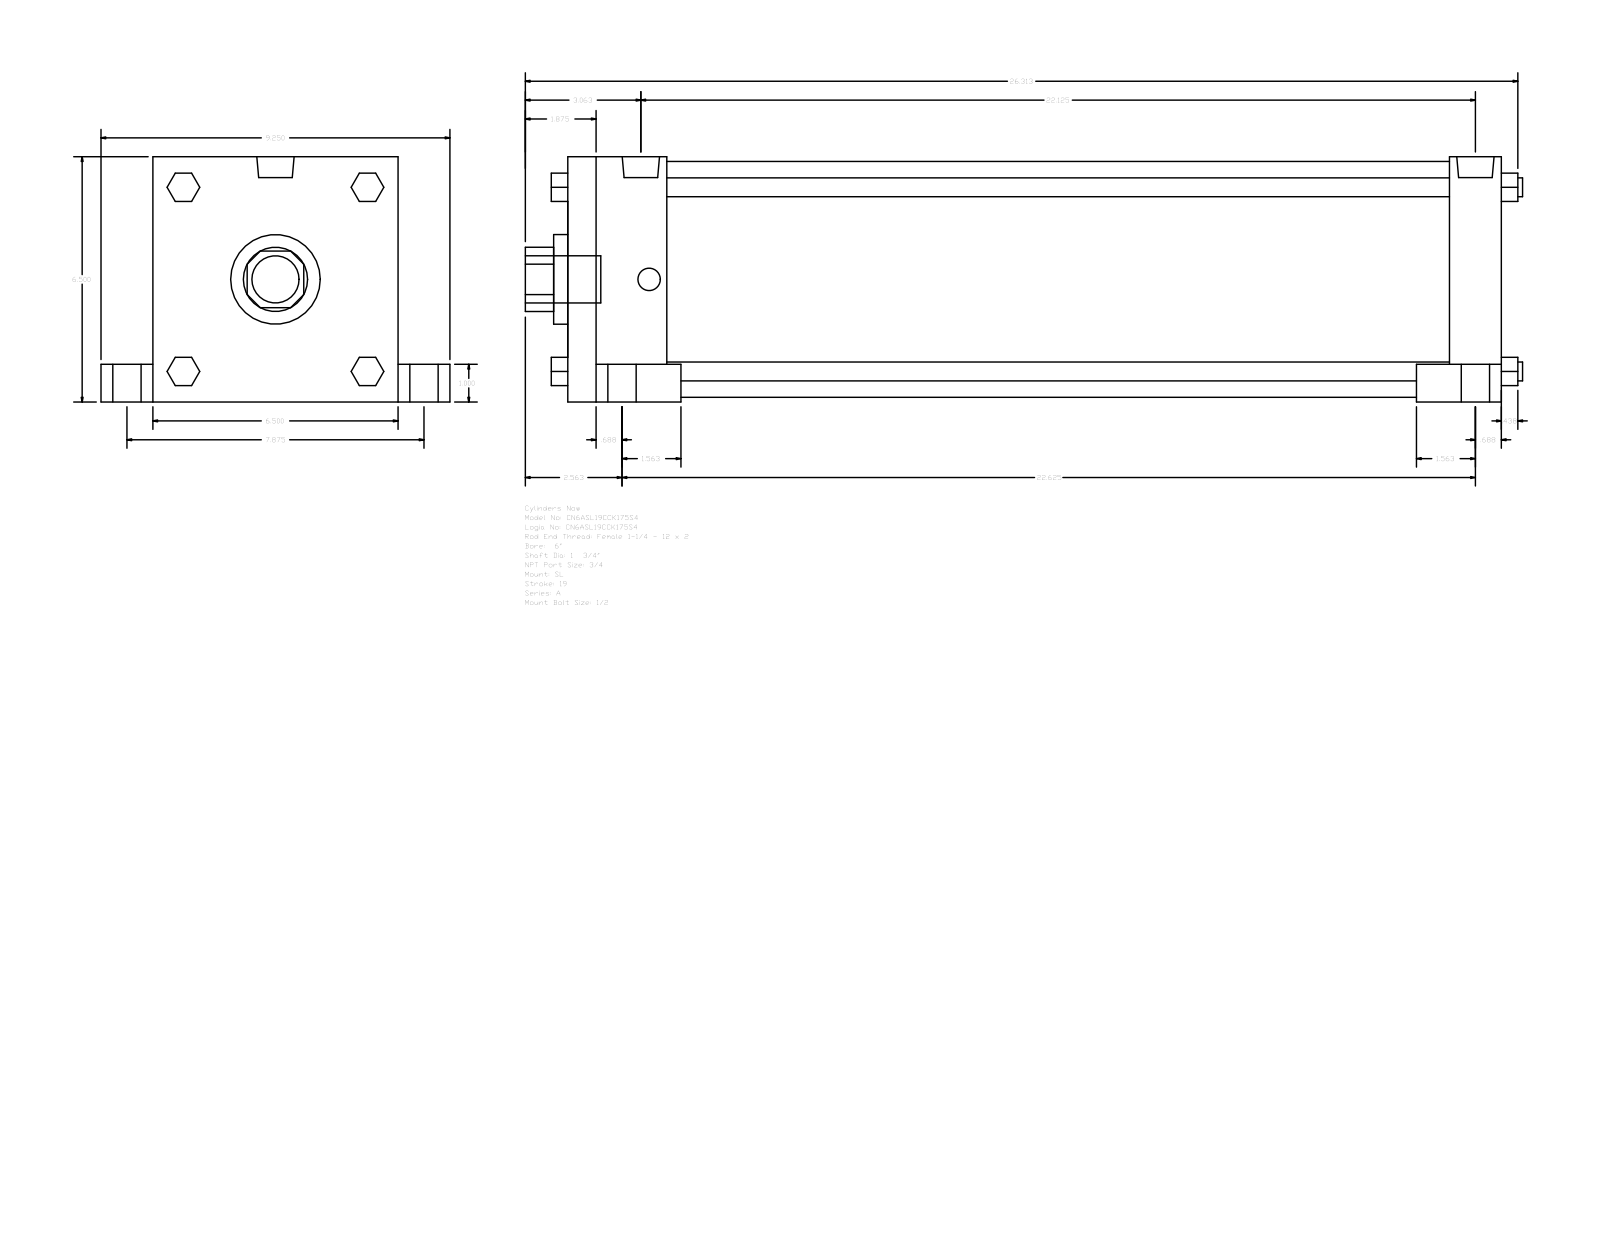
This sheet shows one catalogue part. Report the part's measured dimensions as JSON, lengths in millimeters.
{"part_name": "A_SL__0600_1.75", "step_written_by": "GSSL Pune (CONFIG_CONTROL_DESIGN)", "units": "millimeters", "bodies": {"solids": 0, "faces": 150, "planar": 114, "cylindrical": 36, "other": 0}, "overall_size": [671.51, 234.95, 165.1], "round_holes": [[44.45, 1], [60.33, 1], [158.75, 1]], "round_bosses_or_shafts": [[25.4, 4], [19.05, 4], [15.08, 4], [12.7, 4], [25.12, 2], [31.75, 1]], "partial_cylinders_radius": [[21.63, 1]], "face_to_face_distances": [165.1, 628.66, 66.68, 561.98, 593.73, 527.05, 34.93, 34.92, 25.4, 139.7]}
